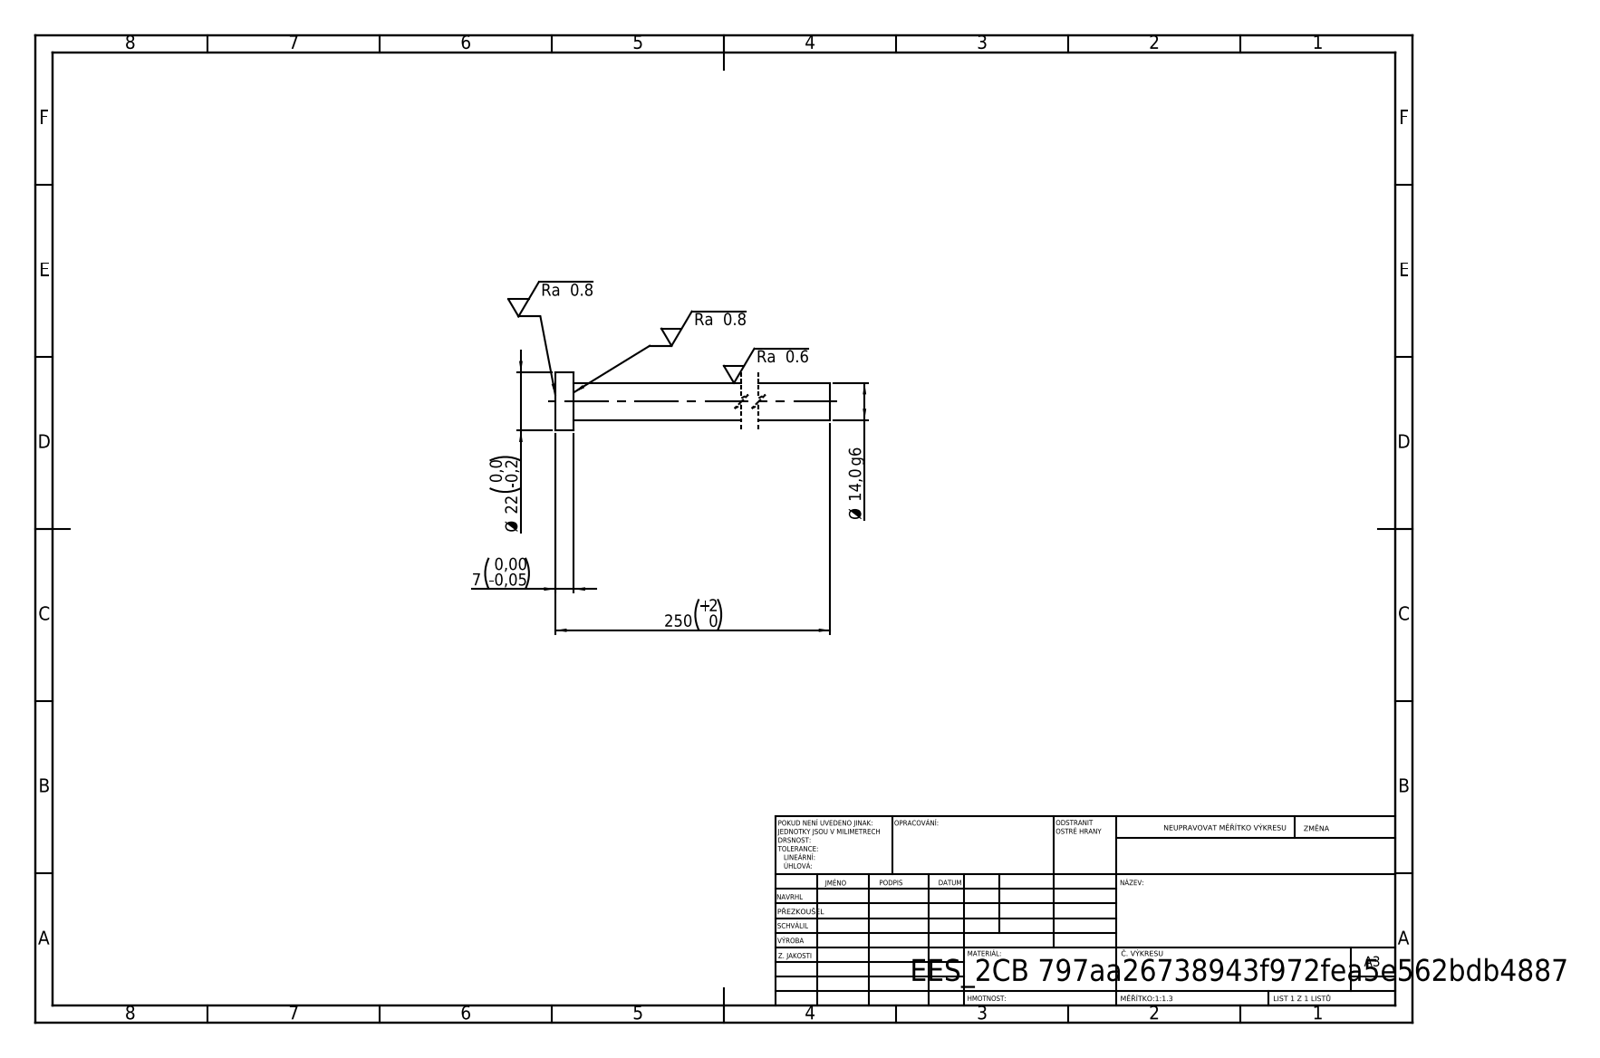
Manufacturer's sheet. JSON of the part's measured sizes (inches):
{"step_written_by": "SolidWorks 2019 (CONFIG_CONTROL_DESIGN)", "units": "inches", "bodies": {"solids": 1, "faces": 7, "planar": 3, "cylindrical": 4, "other": 0}, "overall_size": [9.843, 0.866, 0.866], "volume_in3": 2.445, "surface_area_in2": 18.49, "round_bosses_or_shafts": [[0.866, 1], [0.551, 1]], "face_to_face_distances": [0.276, 9.843, 9.567]}
